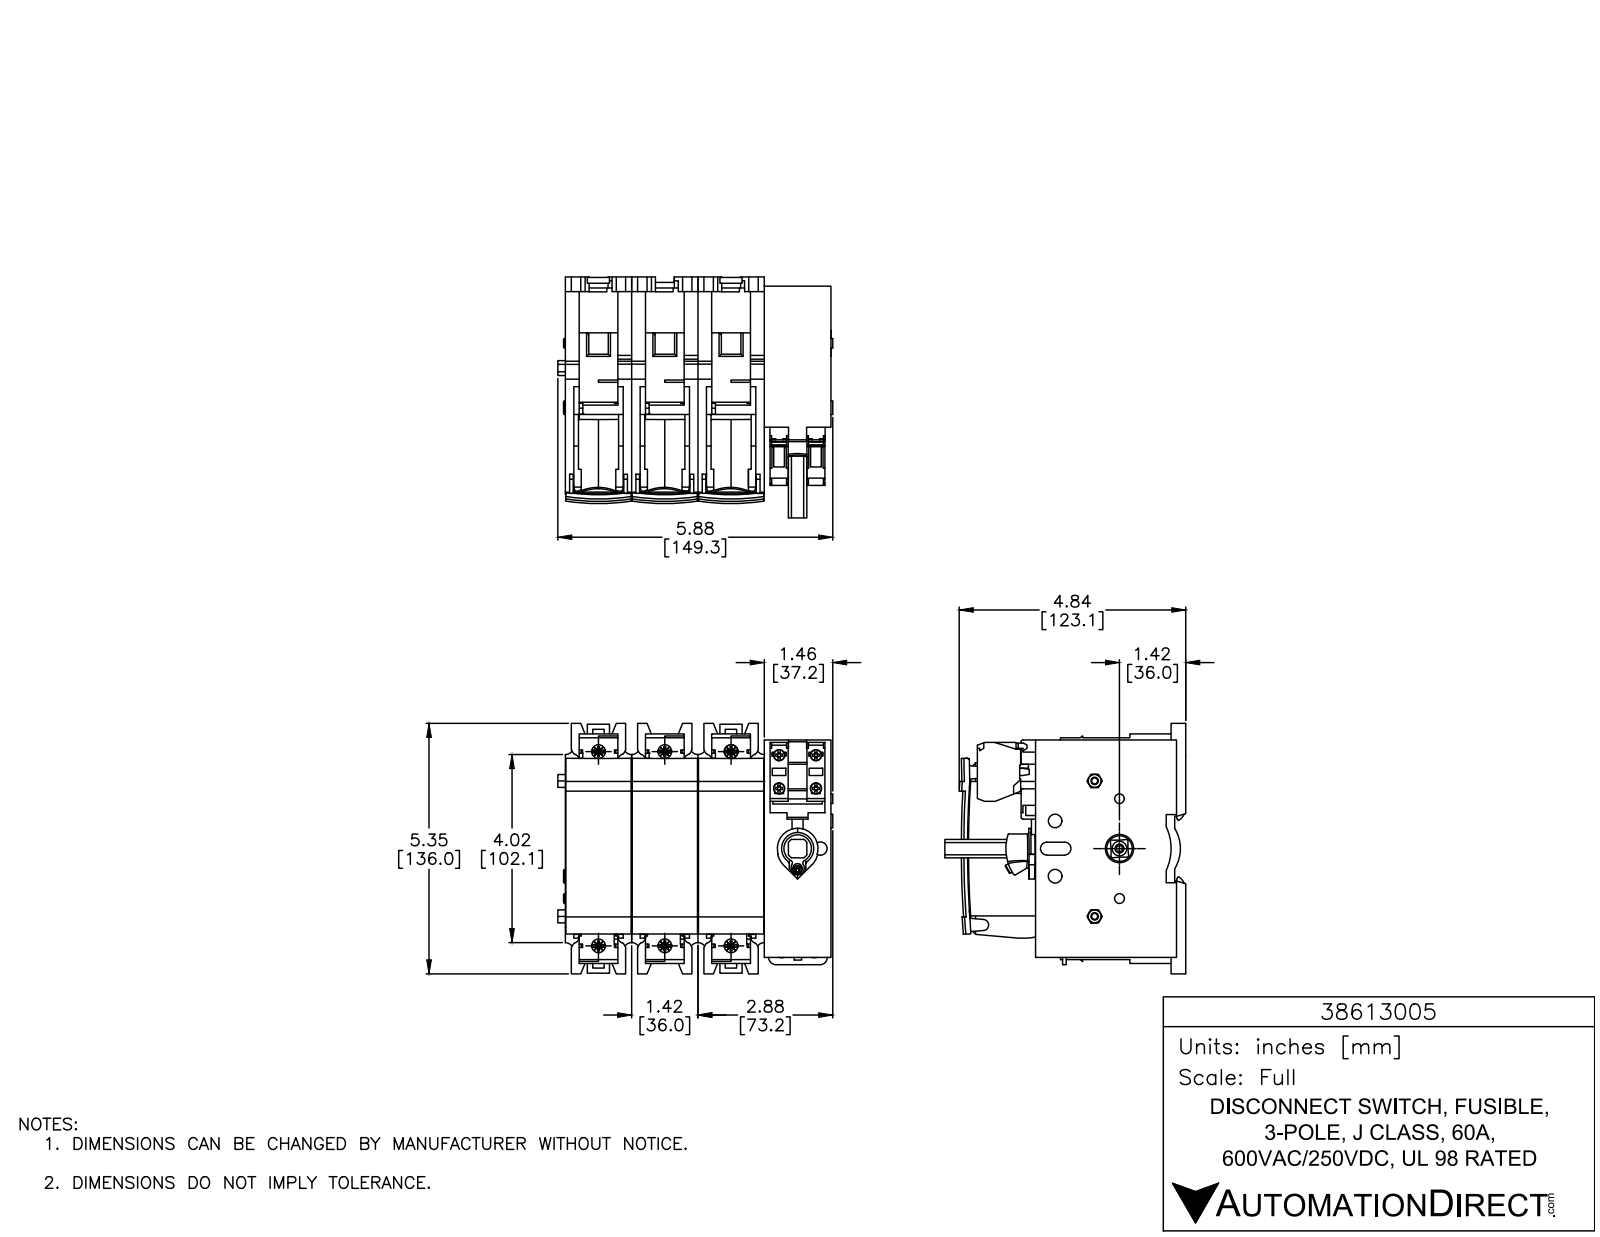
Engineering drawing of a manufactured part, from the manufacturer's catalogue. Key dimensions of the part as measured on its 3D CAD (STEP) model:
Part name (STEP PRODUCT): 38613005
STEP written by: SolidWorks 2015 (AUTOMOTIVE_DESIGN)
Units: inches
Bodies: 13 solids, 2177 faces (1447 planar, 475 cylindrical, 255 other)
Overall size (bounding box): 5.878 × 5.354 × 4.845
Volume: 92.09 in³ · Surface area: 352.4 in²
Round holes (diameter × count): ⌀0.291 ×6, ⌀0.087 ×2, ⌀0.126 ×2, ⌀0.157 ×2, ⌀0.158 ×2, ⌀0.169 ×2, ⌀0.211 ×2, ⌀0.295 ×2, ⌀0.315 ×2, ⌀0.098 ×1, ⌀0.13 ×1, ⌀0.283 ×1
Round bosses / shafts (diameter × count): ⌀0.287 ×2, ⌀0.203 ×2, ⌀0.63 ×1, ⌀0.315 ×1, ⌀0.197 ×1, ⌀0.139 ×1
Partial cylindrical surfaces — rounded edges, fillets, slot ends (radius × count): R0.006 ×68, R0.02 ×12, R0.039 ×11, R0.197 ×7, R0.118 ×4, R0.138 ×3, R0.065 ×2, R0.157 ×2
Main face-to-face distances: 1.417, 2.835, 0.295, 1.122, 4.252, 1.713, 2.539, 1.425, 2.843, 4.26
Hole centre spacings: 1.417, 4.386, 4.15, 0.653, 0.987, 1.067, 1.204, 1.342
